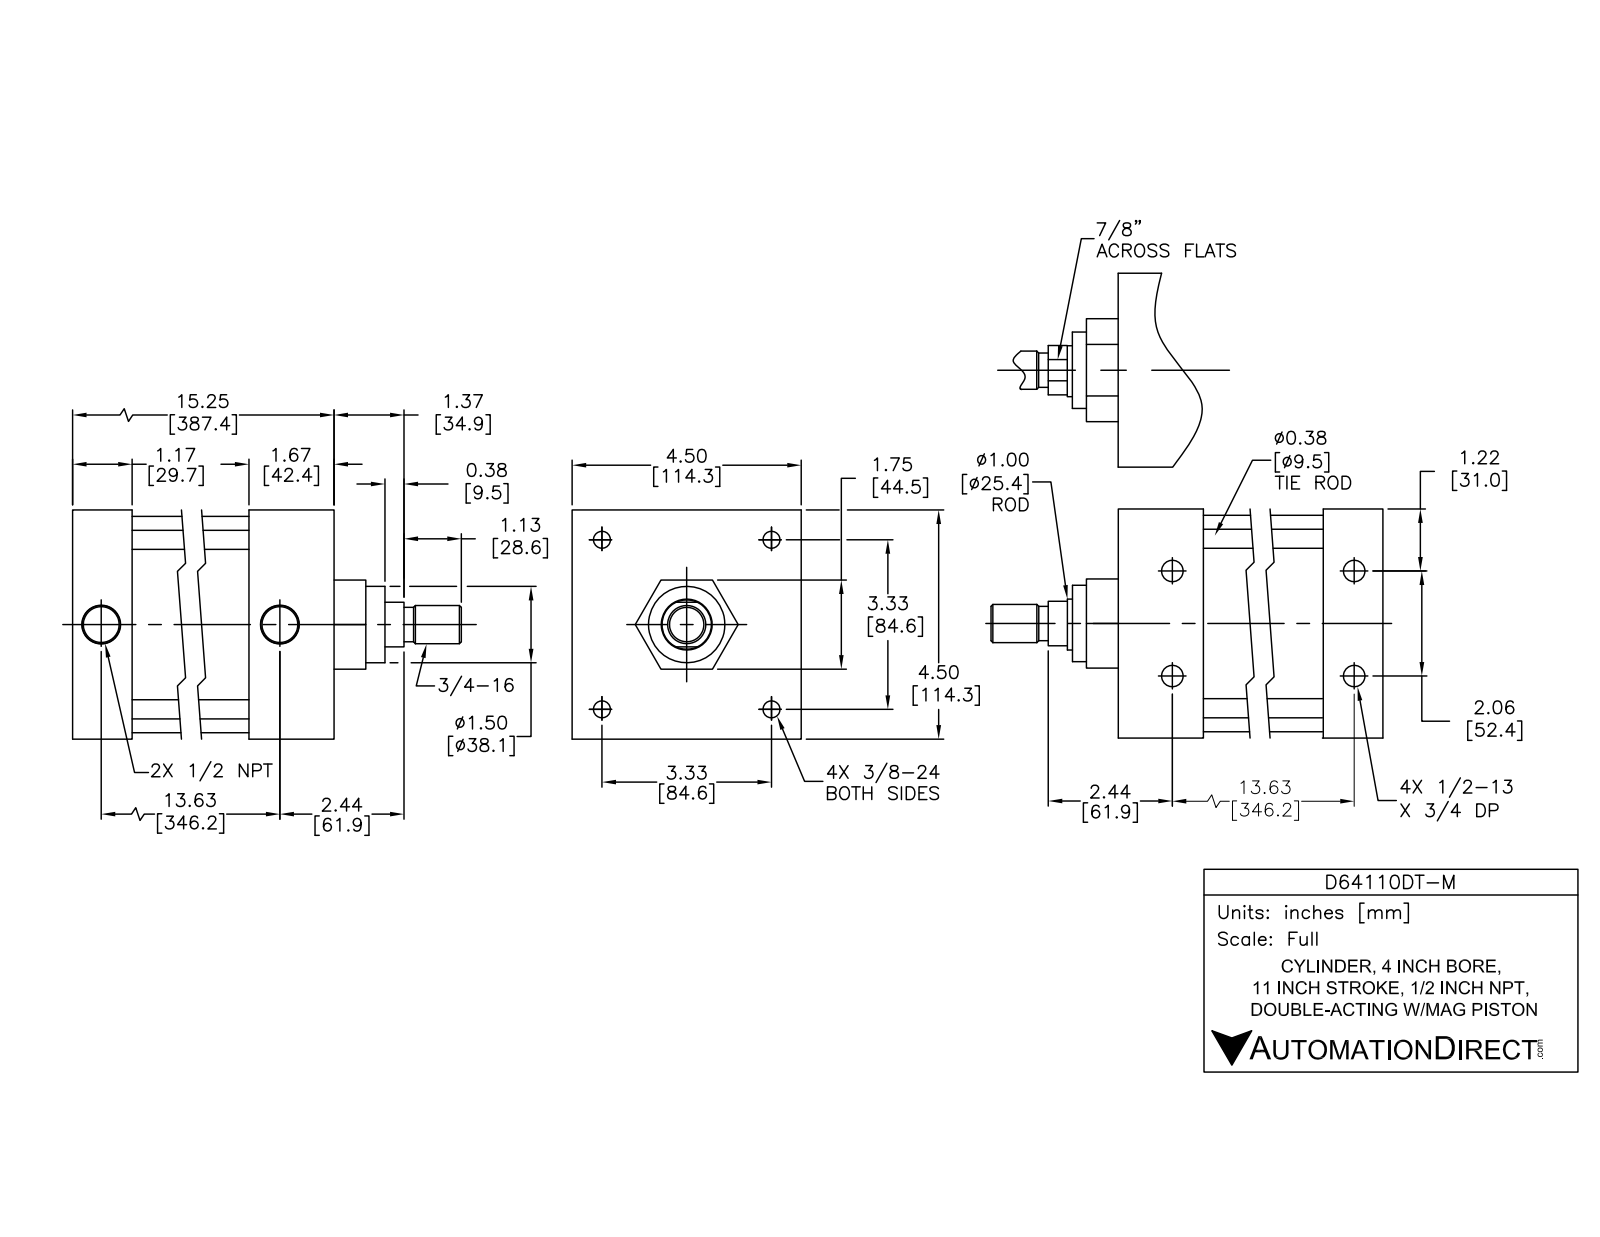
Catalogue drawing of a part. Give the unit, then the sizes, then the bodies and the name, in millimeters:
Units: millimetres
Overall size (bounding box): 450.7 × 114.3 × 114.3
Round holes (diameter × count): ⌀8.4 ×4, ⌀10.3 ×4, ⌀10.6 ×4, ⌀15.9 ×4, ⌀12.7 ×2, ⌀19.5 ×2, ⌀25.4 ×1, ⌀25.5 ×1, ⌀101.6 ×1
Round bosses / shafts (diameter × count): ⌀15.5 ×4, ⌀9.5 ×4, ⌀8.6 ×4, ⌀108 ×1, ⌀101.5 ×1, ⌀44.5 ×1, ⌀25.3 ×1, ⌀24.6 ×1
Partial cylindrical surfaces — rounded edges, fillets, slot ends (radius × count): R11.4 ×4
Main face-to-face distances: 114.3, 387.2, 44.5, 355.5, 31.7, 323.9, 31.6, 63.4, 355.5, 31.6
Hole centre spacings: 59.7, 84.4, 347, 346, 26.2, 26.2, 52.4, 119.3
Volume: 1 765 000 mm³ · Surface area: 423 800 mm²
Bodies: 12 solids, 303 faces (99 planar, 114 cylindrical, 90 other)
Part name (STEP PRODUCT): D64110DT-M PISTON; D64110DT-M BODY; D64110DT-M
STEP written by: SolidWorks 2015 (AUTOMOTIVE_DESIGN)
